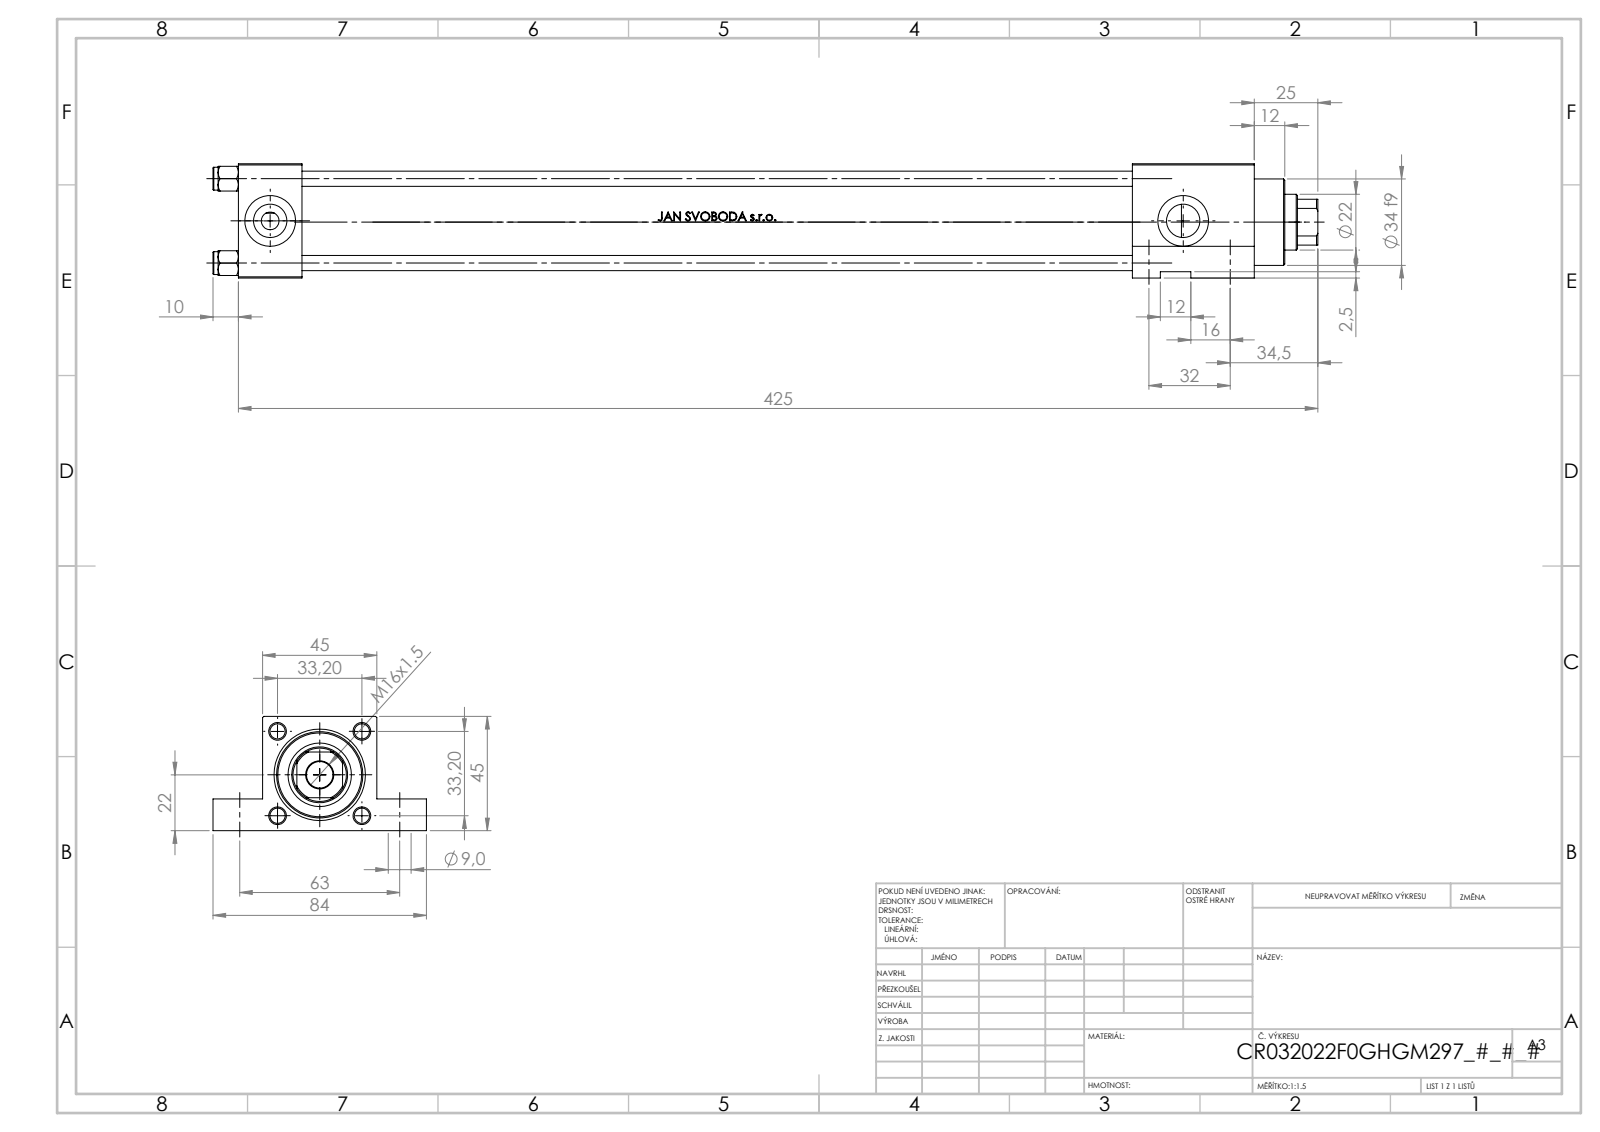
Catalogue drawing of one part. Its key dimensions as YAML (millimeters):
part_name: "V215_VC_A; V215CR_F_Body; V215CR_F_TYCINKA; NUT_M5_F (+1 more)"
step_written_by: "SolidWorks 2019 (CONFIG_CONTROL_DESIGN)"
units: millimeters
bodies: {solids: 11, faces: 1102, planar: 436, cylindrical: 126, other: 540}
overall_size: [435, 84, 45]
volume: 456207
surface_area: 177748
round_holes:
  - {diameter: 6, count: 4}
  - {diameter: 9, count: 4}
  - {diameter: 7, count: 2}
  - {diameter: 13.16, count: 2}
  - {diameter: 20, count: 2}
  - {diameter: 10.5, count: 1}
  - {diameter: 22, count: 1}
  - {diameter: 24, count: 1}
  - {diameter: 25, count: 1}
  - {diameter: 32, count: 1}
  - {diameter: 33, count: 1}
round_bosses_or_shafts:
  - {diameter: 9, count: 4}
  - {diameter: 38, count: 1}
  - {diameter: 34, count: 1}
partial_cylinders:
  - {radius: 10.5, count: 1}
face_to_face_distances: [45, 25, 375, 400, 352, 327, 12.5, 32.5, 48, 10]
hole_center_spacings: [33.2, 23.13, 23.83, 32, 46.95, 63, 70.66, 359.5]
